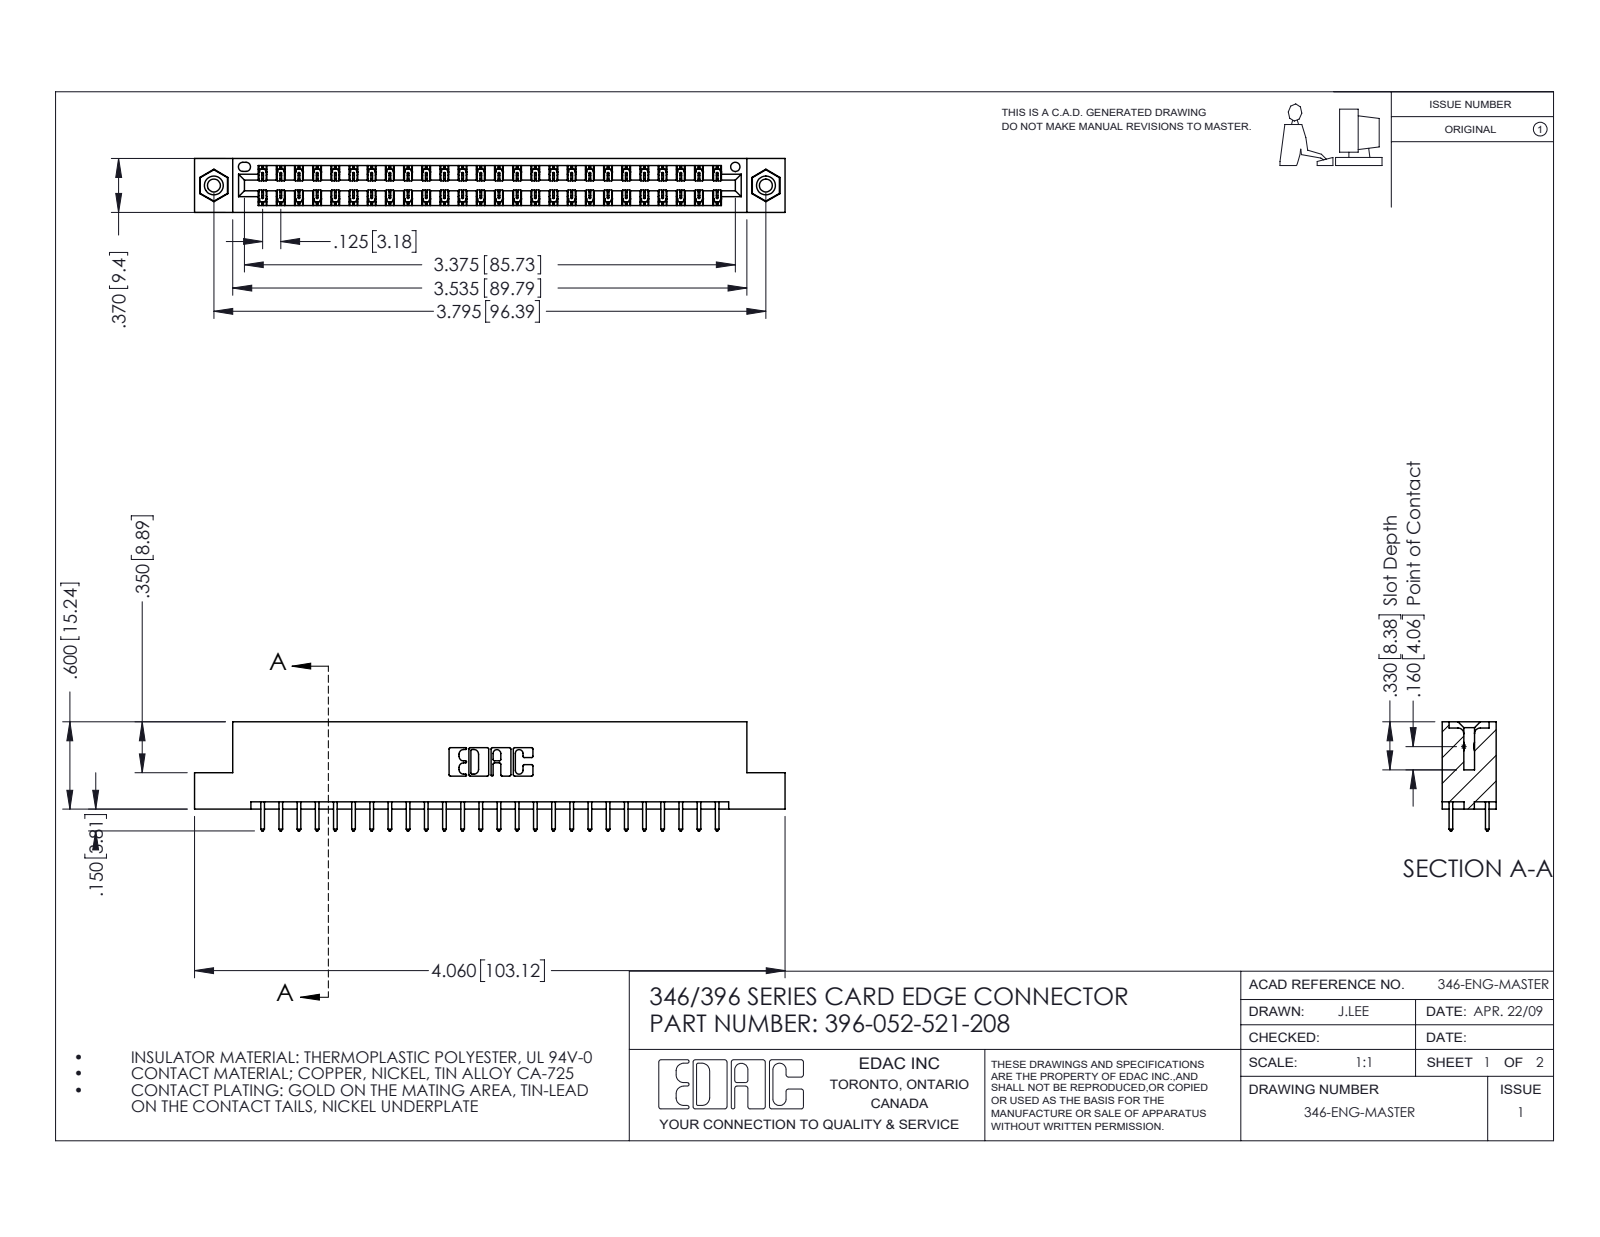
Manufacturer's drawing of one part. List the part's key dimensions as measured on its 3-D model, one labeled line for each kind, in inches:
Part name (STEP PRODUCT): 345-292-001_345-293-121; 346 Part_Flush Mounting Lugs - 0.156 Dia-TI; 396-052-521-208; 345-250-001_345-250-003-102
STEP written by: SolidWorks 2016 (CONFIG_CONTROL_DESIGN)
Units: inches
Bodies: 55 solids, 2886 faces (1928 planar, 942 cylindrical, 16 other)
Overall size (bounding box): 4.06 × 0.75 × 0.37
Volume: 0.604 in³ · Surface area: 20.52 in²
Round holes (diameter × count): ⌀0.089 ×2, ⌀0.125 ×2, ⌀0.156 ×2, ⌀0.064 ×1
Round bosses / shafts (diameter × count): ⌀0.155 ×2
Partial cylindrical surfaces — rounded edges, fillets, slot ends (radius × count): R0.006 ×78, R0.01 ×52, R0.01 ×22, R0.007 ×6, R0.031 ×6, R0.026 ×3, R0.014 ×2, R0.022 ×2
Main face-to-face distances: 0.048, 0.322, 0.25, 0.37, 0.072, 0.298, 0.025, 0.275, 0.148, 0.222
Hole centre spacings: 0.246, 3.587, 3.795
